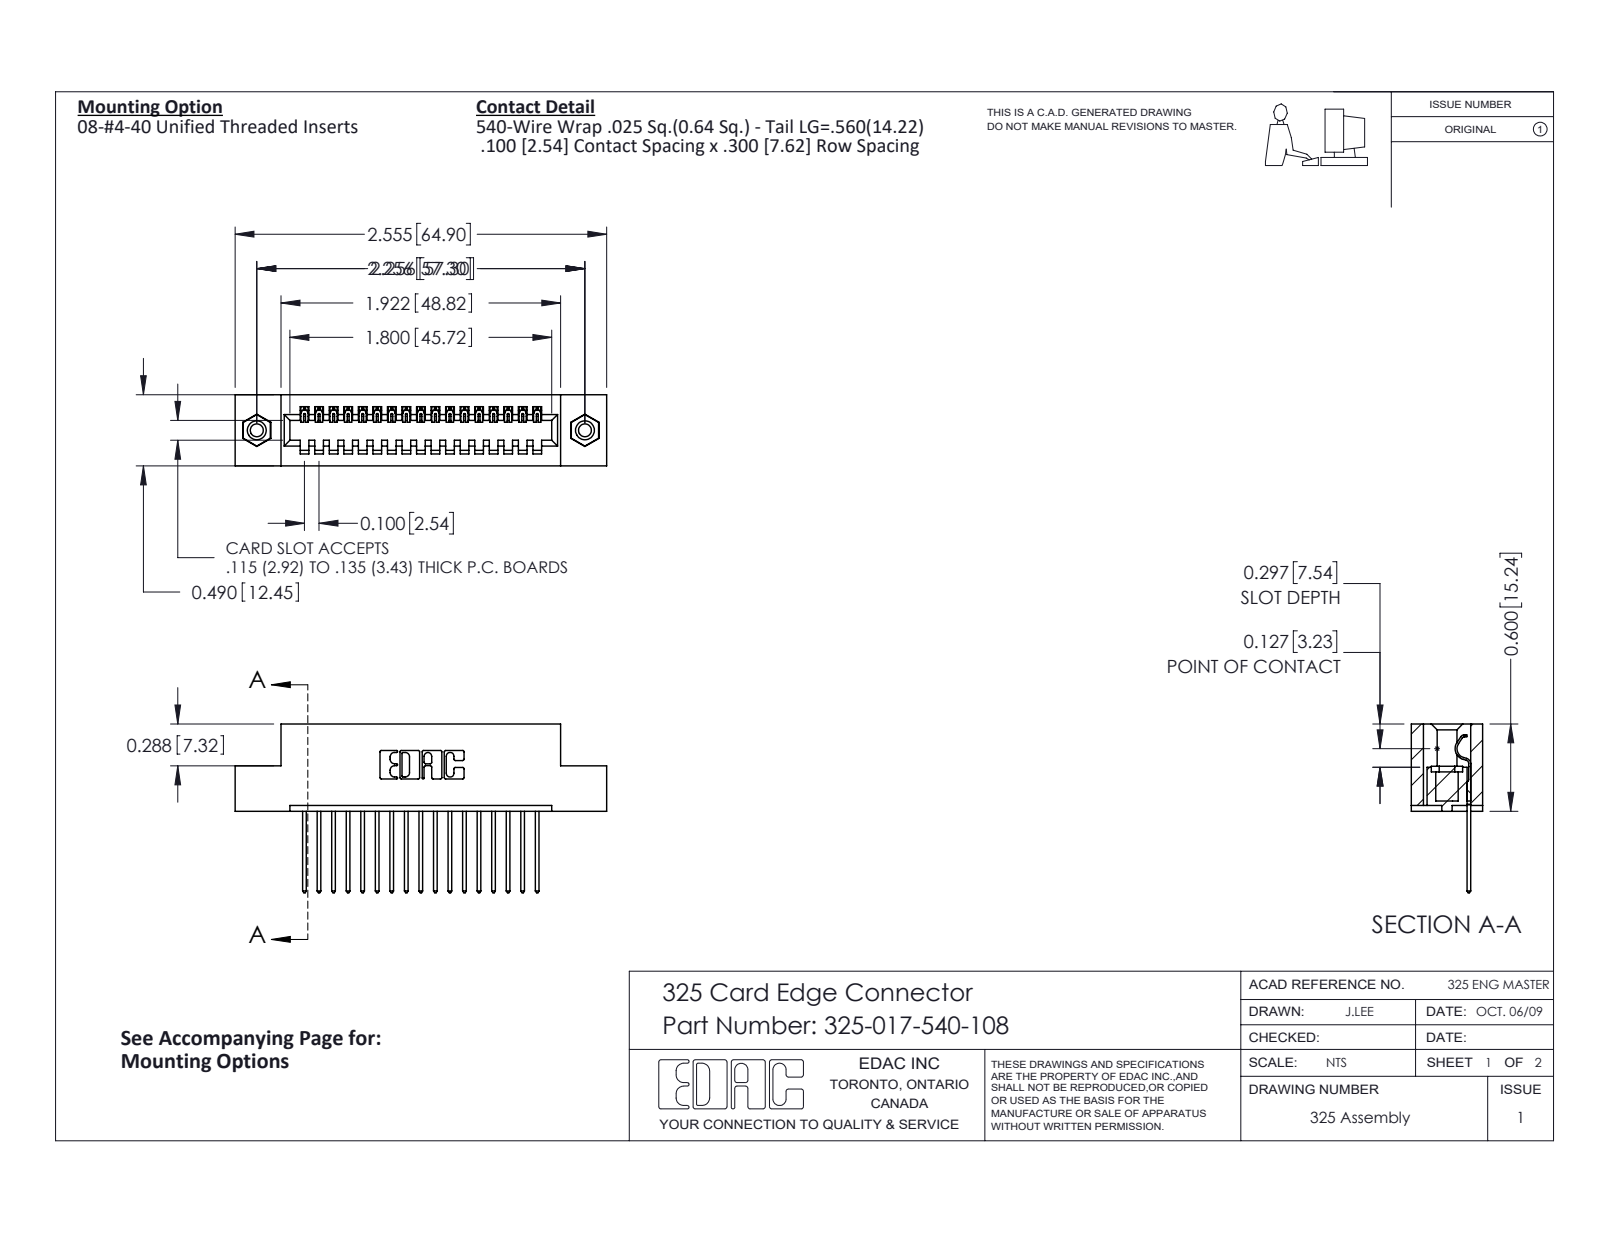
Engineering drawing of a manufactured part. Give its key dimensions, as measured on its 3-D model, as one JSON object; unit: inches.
{"part_name": "345-250-001_345-250-003-102; 325-017-540-108; 325 Part_TI; 325-292-001_325-293-140", "step_written_by": "SolidWorks 2016 (CONFIG_CONTROL_DESIGN)", "units": "inches", "bodies": {"solids": 20, "faces": 1160, "planar": 816, "cylindrical": 328, "other": 16}, "overall_size": [2.555, 1.16, 0.49], "volume_in3": 0.492, "surface_area_in2": 13.28, "round_holes": [[0.089, 2], [0.125, 2], [0.16, 2]], "round_bosses_or_shafts": [[0.155, 2]], "partial_cylinders_radius": [[0.006, 34], [0.01, 34], [0.01, 22], [0.007, 6], [0.031, 6], [0.026, 3], [0.014, 1], [0.022, 1]], "face_to_face_distances": [0.083, 0.407, 0.3, 0.49, 0.107, 0.383, 0.025, 0.6, 0.04, 0.2], "hole_center_spacings": [2.256]}
